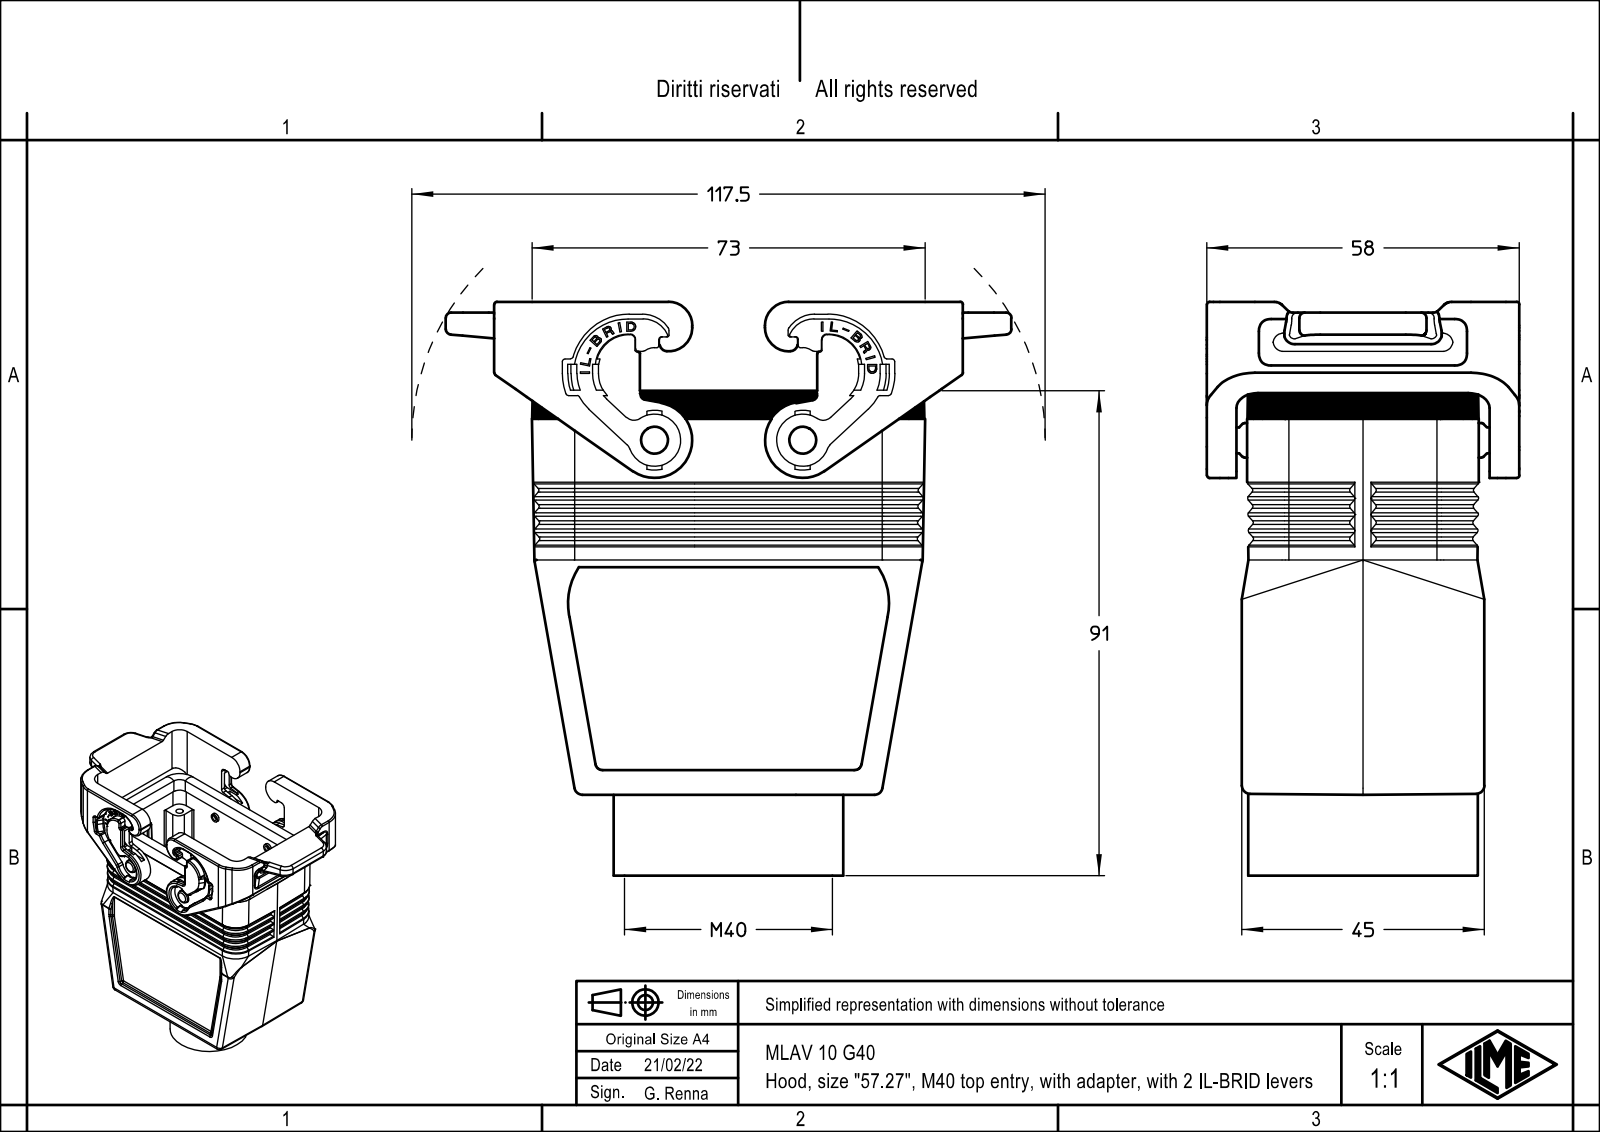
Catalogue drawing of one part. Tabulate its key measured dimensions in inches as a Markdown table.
| quantity | value |
| --- | --- |
| part name | MLAV_10_G40 |
| STEP written by | Creo Elements/Direct Modeling 20.1B 02-Apr-2019 (C) Parametric Technology GmbH (AUTOMOTIVE_DESIGN) |
| units | inches |
| bodies | 1 solid, 1497 faces (966 planar, 339 cylindrical, 192 other) |
| overall size | 4.348 × 4.134 × 2.283 |
| volume | 6.338 in³ |
| surface area | 84.58 in² |
| round holes (diameter × count) | 0.108 × 4, 1.339 × 1, 1.575 × 1 |
| round bosses / shafts (diameter × count) | 0.268 × 2, 0.189 × 2, 1.811 × 1 |
| partial cylindrical surfaces (radius × count) | 0.039 × 54, 0.02 × 43, 0.118 × 20, 0.276 × 16, 0.013 × 15, 0.059 × 14, 0.012 × 8, 0.079 × 8 |
| main face-to-face distances | 1.545, 0.079, 0.148, 0.226, 0.039, 1.772, 1.624, 1.693, 0.187, 1.585 |
| hole center spacings | 1.242, 1.063, 2.244, 2.483 |
